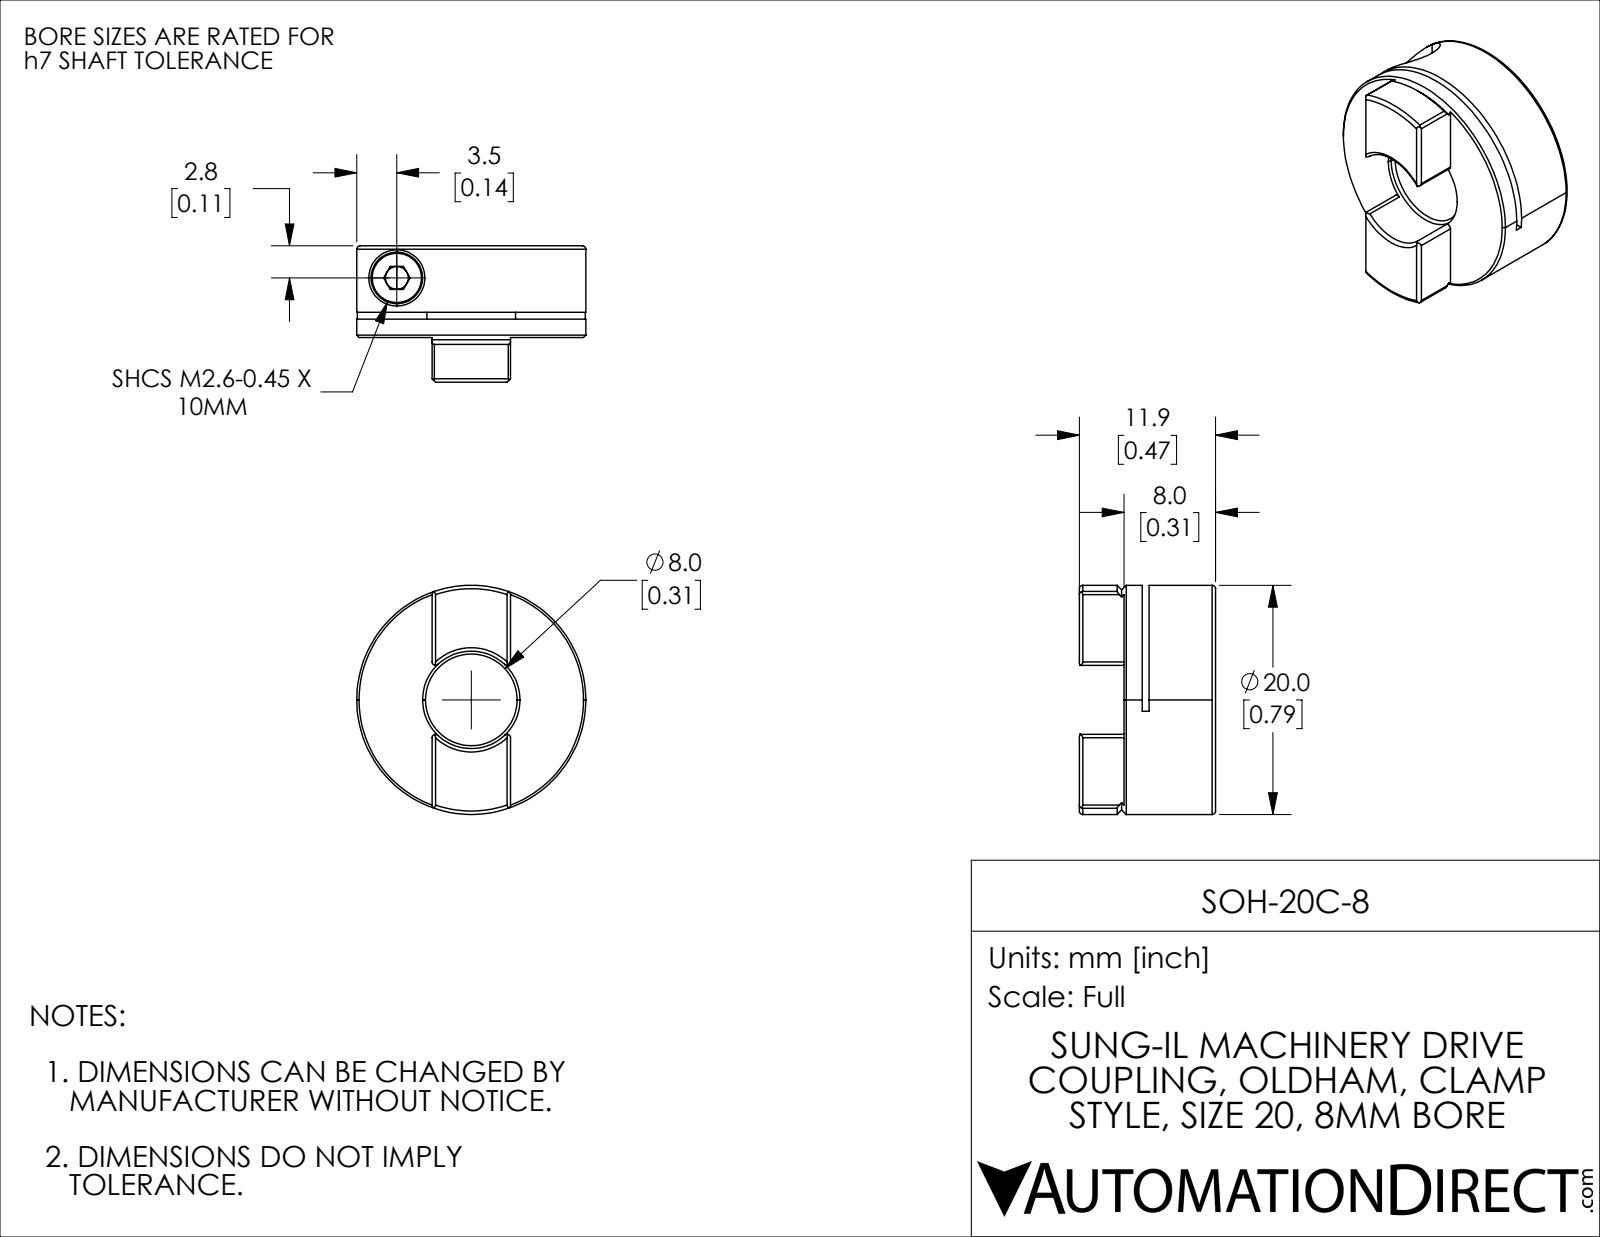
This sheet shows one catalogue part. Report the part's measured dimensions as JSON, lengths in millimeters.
{"part_name": "SOH-20C-8", "step_written_by": "SolidWorks 2021 (CONFIG_CONTROL_DESIGN)", "units": "millimeters", "bodies": {"solids": 2, "faces": 96, "planar": 38, "cylindrical": 33, "other": 25}, "overall_size": [20, 20, 11.9], "volume_mm3": 2247, "surface_area_mm2": 2009, "round_holes": [[2, 1], [2.05, 1], [2.8, 1], [4.9, 1], [8, 1], [8.5, 1]], "round_bosses_or_shafts": [[20, 1], [4.5, 1], [2.6, 1]], "partial_cylinders_radius": [[0.3, 8], [22.5, 1]], "face_to_face_distances": [8, 5.8, 6.4, 1.6, 0.6, 2.2, 11.9, 6.1, 5.5, 3.9]}
